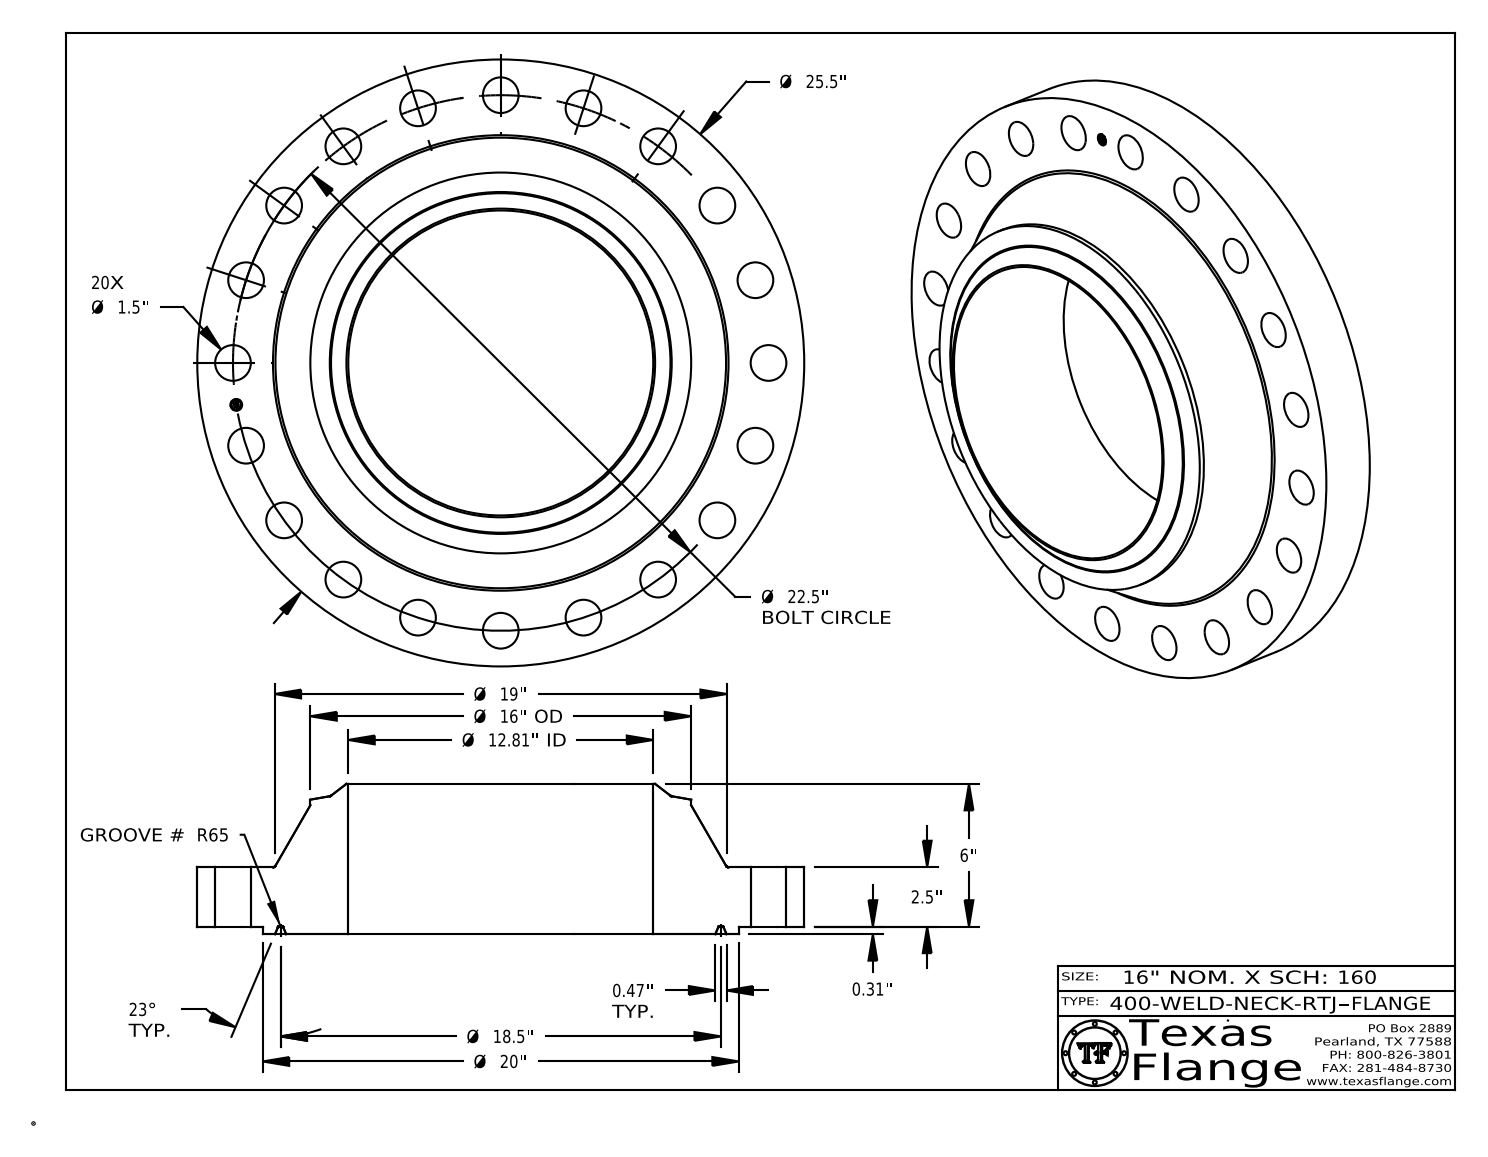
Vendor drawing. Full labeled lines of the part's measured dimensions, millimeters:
Part name (STEP PRODUCT): 400-WELD-NECK-RTJ
STEP written by: CATIA V5 STEP AP214 (AUTOMOTIVE_DESIGN)
Units: millimetres
Bodies: 1 solid, 457 faces (371 planar, 68 cylindrical, 18 other)
Overall size (bounding box): 647.7 × 647.7 × 160.4
Volume: 20 370 000 mm³ · Surface area: 985 800 mm²
Round holes (diameter × count): ⌀38.1 ×20, ⌀12.6 ×1, ⌀325.4 ×1
Round bosses / shafts (diameter × count): ⌀0.8 ×8, ⌀647.7 ×1, ⌀508 ×1, ⌀406.4 ×1, ⌀9.9 ×1
Main face-to-face distances: 63.5, 8, 71.5, 160.4, 152.4, 88.9, 71.1, 63.1, 0.4, 89.3
Hole centre spacings: 285.8, 176.6, 335.9, 89.4, 462.4, 509.2, 543.5, 564.5
